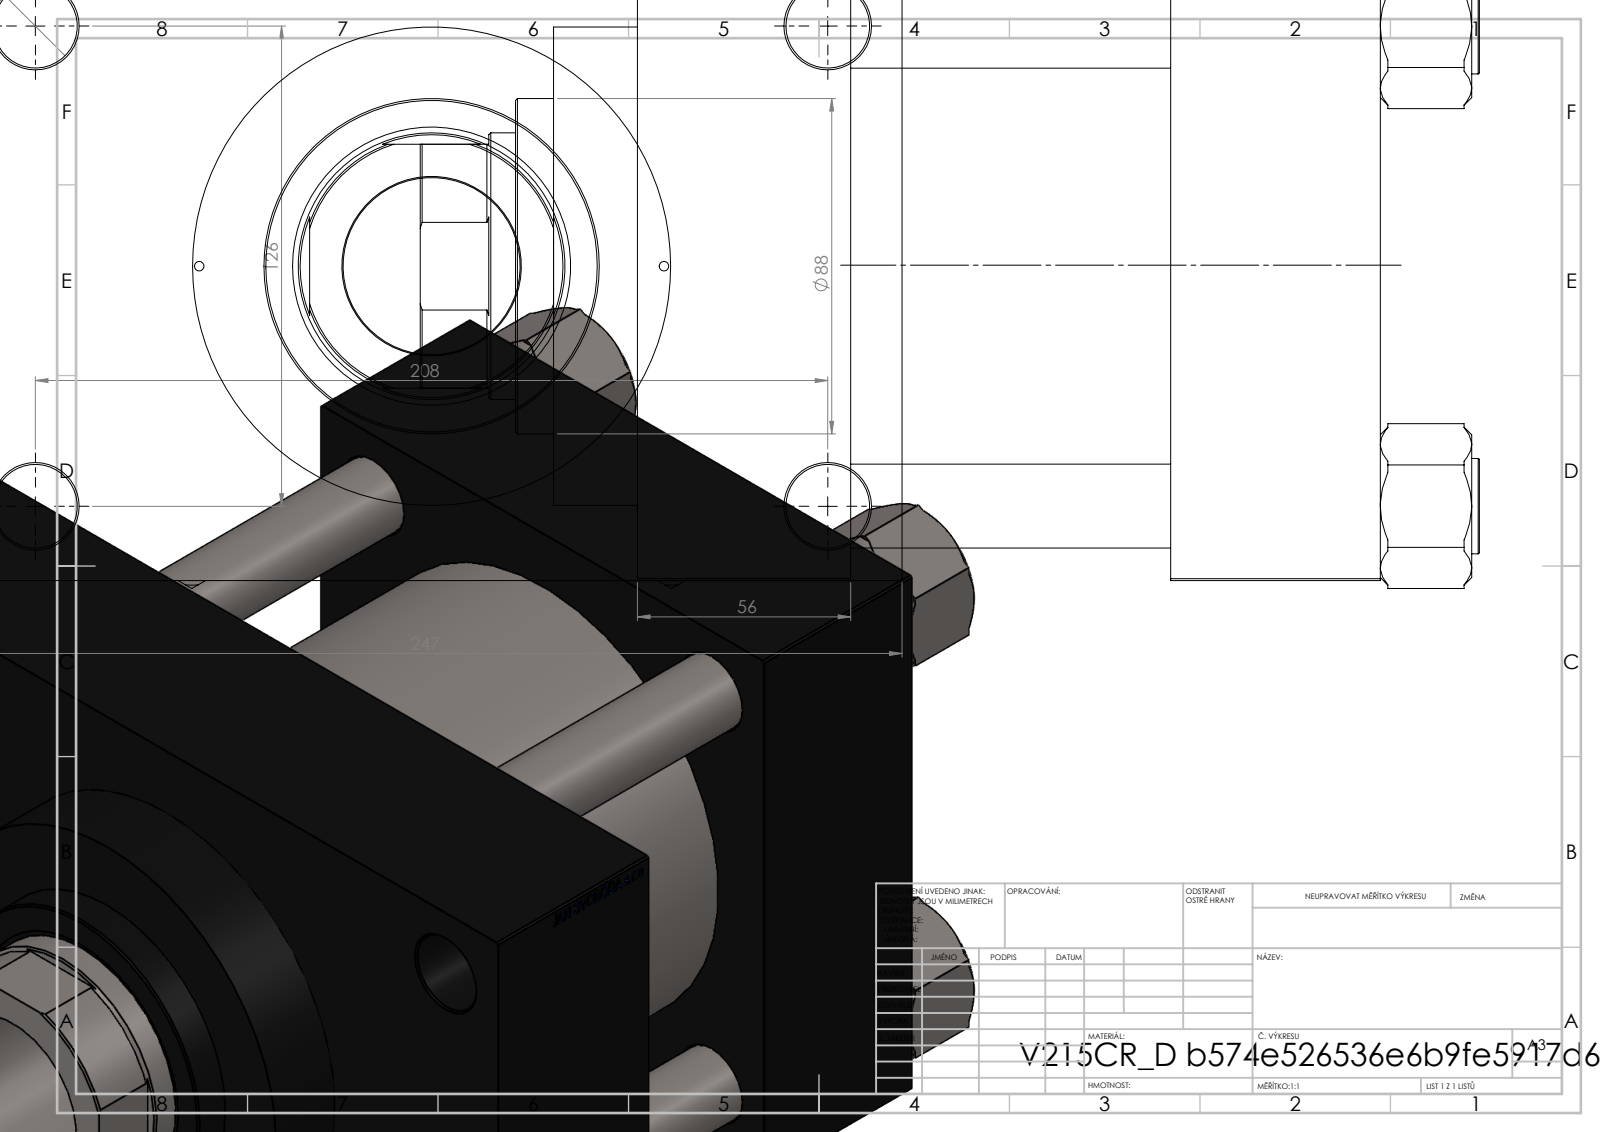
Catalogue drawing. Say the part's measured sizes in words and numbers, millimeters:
The part is named "V215CR_D_TYCINKA; V215CR_VCP_D; V215CR_D_Body; NUT_M5_D (+1 more)". Its 3-D file was written by "SolidWorks 2019 (CONFIG_CONTROL_DESIGN)". It is 11 solids with 1154 faces: 546 planar, 90 cylindrical and 518 other. Overall it measures 278 by 247 by 169.14 millimeters. Its volume is 5 013 000 cubic millimeters and its surface area 542 220 square millimeters. Round holes: 8 of diameter 22, 2 of diameter 2.5, 2 of diameter 7, 2 of diameter 32.24, 2 of diameter 45, 1 of diameter 46.5, 1 of diameter 70, 1 of diameter 73, 1 of diameter 96, 1 of diameter 125, 1 of diameter 125.5. Round bosses or shafts: 4 of diameter 25, 1 of diameter 131, 1 of diameter 88. Partial cylindrical surfaces (rounded edges, fillets, slot ends): 1 of radius 34. The main face-to-face distances are 165, 84, 55, 139, 195, 140, 56, 41, 206, 173.74. The hole center spacings are 41.05, 62.98, 76.28, 89.02, 121.59, 125.9, 132.47, 139.02.
